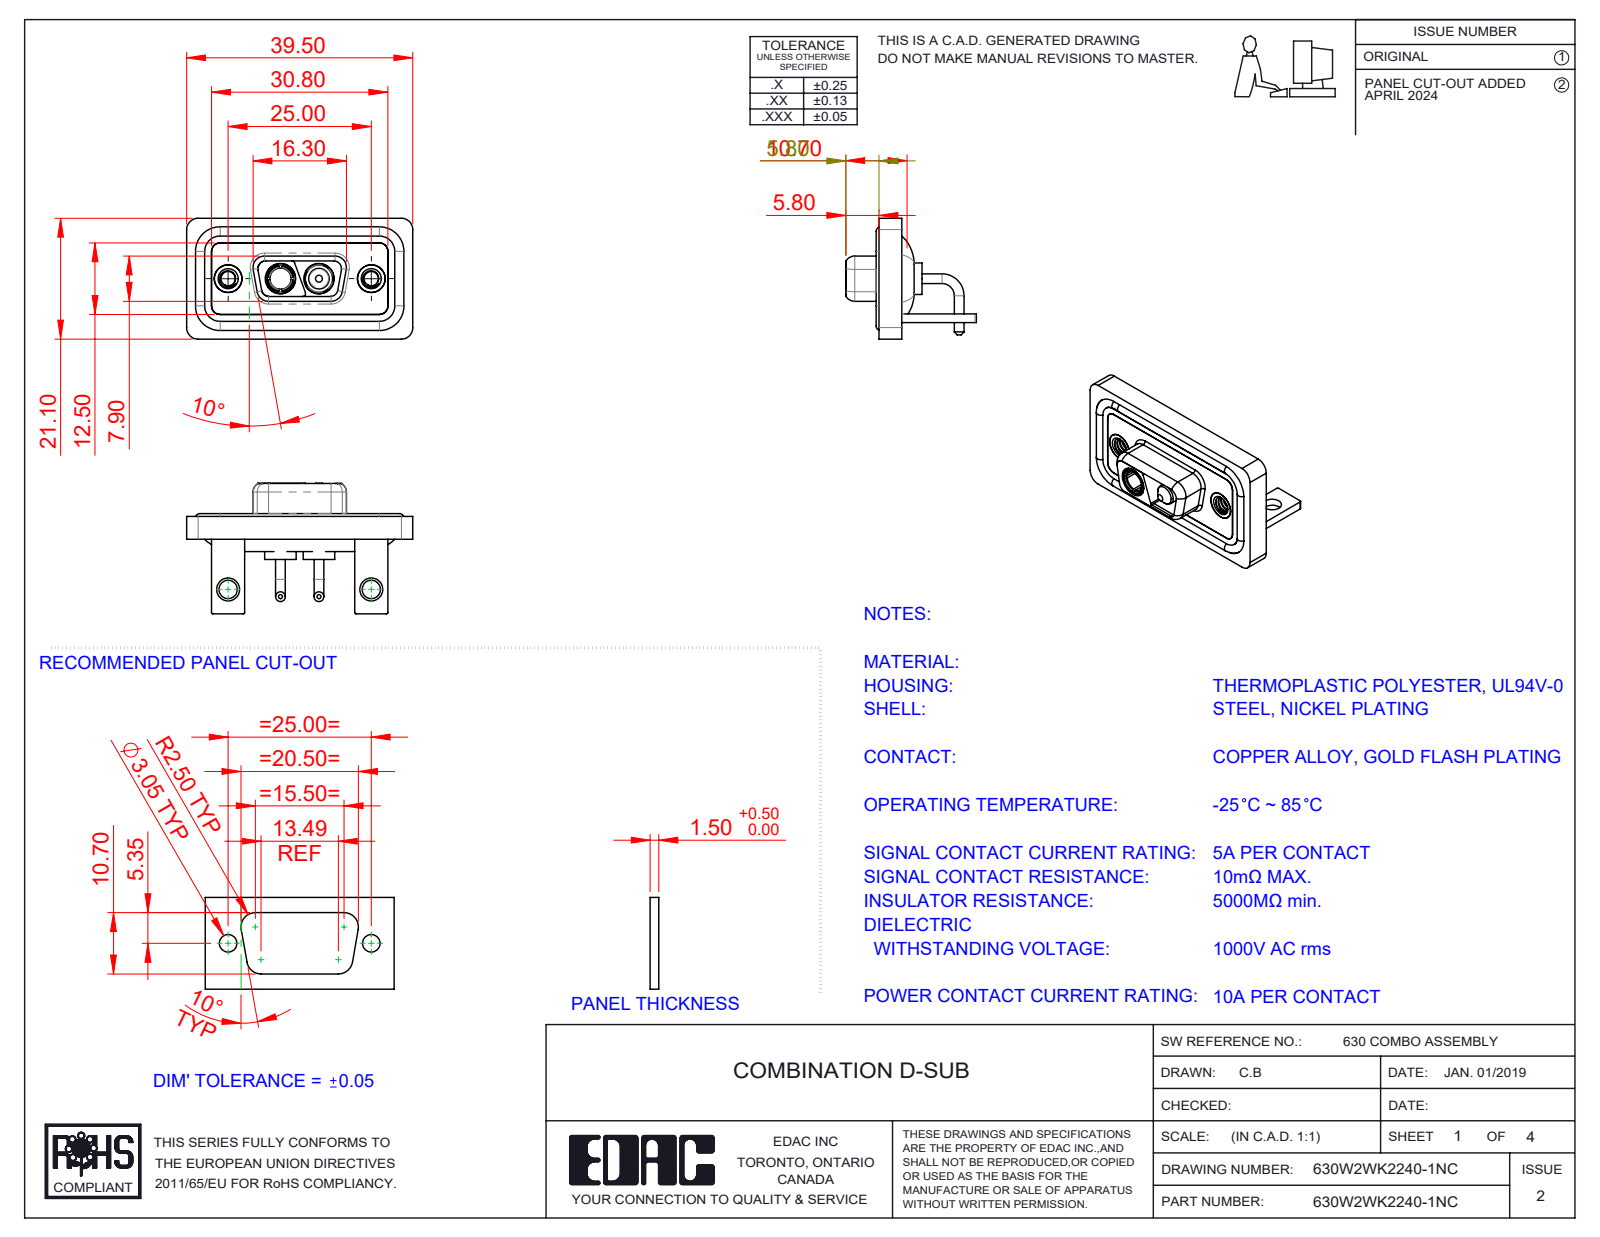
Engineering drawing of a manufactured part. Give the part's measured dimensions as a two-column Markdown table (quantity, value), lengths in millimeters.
| quantity | value |
| --- | --- |
| part name | 630Combo Shell Front_09 Contacts; 630Combo Shell Rear_09 Contacts; 630Combo Housing_2WK2; Power Socket_10A RA (+5 more) |
| STEP written by | SolidWorks 2023 (CONFIG_CONTROL_DESIGN) |
| units | millimeters |
| bodies | 13 solids, 550 faces (164 planar, 257 cylindrical, 129 other) |
| overall size | 39.5 × 22.8 × 21.1 |
| volume | 4 950 mm³ |
| surface area | 8 131 mm² |
| round holes (diameter × count) | 4.85 × 4, 2.5 × 2, 3.2 × 2, 4 × 2, 4.05 × 2, 5 × 2, 5.3 × 2, 3.7 × 1 |
| round bosses / shafts (diameter × count) | 1.7 × 4, 1.6 × 4, 5.5 × 2, 5.2 × 2, 4.95 × 2, 4.8 × 2, 4.75 × 2, 3.75 × 2 |
| partial cylindrical surfaces (radius × count) | 2 × 19, 1.5 × 18, 0.25 × 16, 1.35 × 8, 1.6 × 8, 0.5 × 7, 0.6 × 4, 0.65 × 4 |
| main face-to-face distances | 0.4, 2.9, 1.5, 1.1, 3.7, 1.8, 0.8, 2.5, 1.6, 3.1 |
| hole center spacings | 9.14, 15.86, 25, 6.72 |
